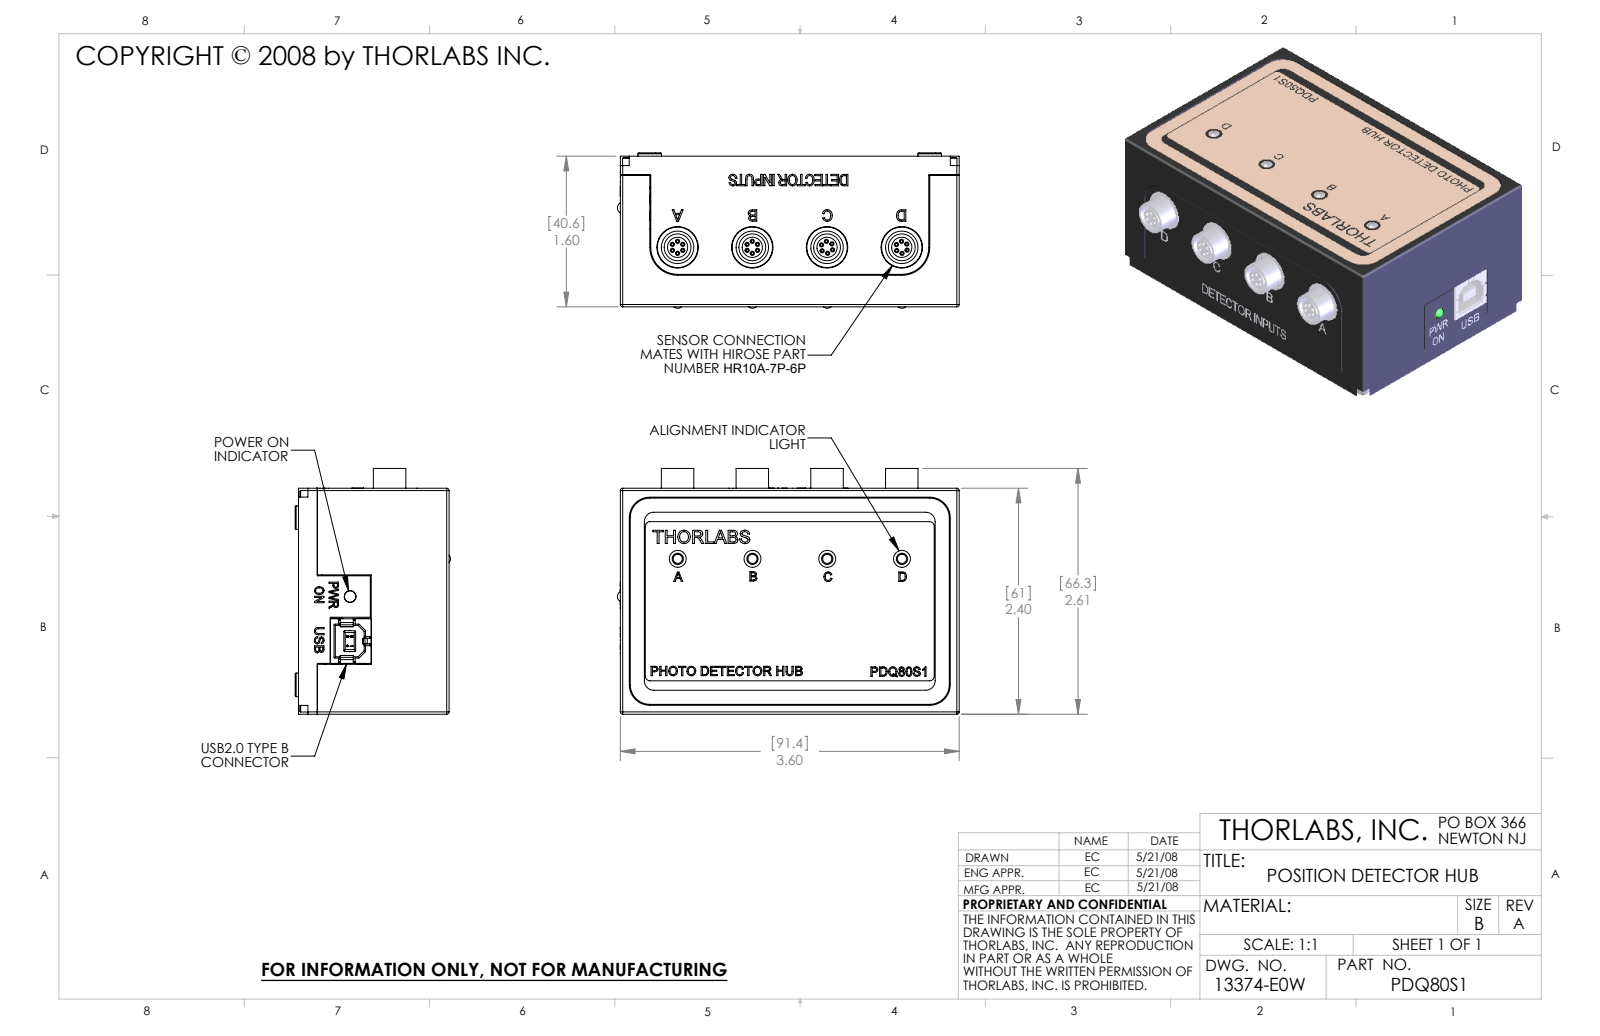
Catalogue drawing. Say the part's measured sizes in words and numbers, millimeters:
The part is named "13374-E0W". Its 3-D file was written by "SolidWorks 2007 (CONFIG_CONTROL_DESIGN)". It is 17 solids with 2142 faces: 1275 planar, 369 cylindrical and 498 other. Overall it measures 92.23 by 66.29 by 41.91 millimeters. Its volume is 57 288 cubic millimeters and its surface area 61 288 square millimeters. Round holes: 12 of diameter 0.63, 12 of diameter 0.64, 6 of diameter 1.78, 6 of diameter 2.18, 4 of diameter 2.39, 4 of diameter 2.84, 4 of diameter 3.05, 4 of diameter 3.3, 4 of diameter 6.35, 4 of diameter 6.6, 4 of diameter 7.24, 4 of diameter 8.2. Round bosses or shafts: 4 of diameter 10.92, 4 of diameter 8.76, 4 of diameter 4.57, 4 of diameter 3.56, 3 of diameter 5.46, 1 of diameter 5.46, 1 of diameter 3.91, 1 of diameter 3.51. Partial cylindrical surfaces (rounded edges, fillets, slot ends): 20 of radius 0.25, 8 of radius 0.13, 8 of radius 0.64, 8 of radius 4.13, 7 of radius 5.4, 6 of radius 1.27, 4 of radius 0.2, 4 of radius 0.3. The main face-to-face distances are 40.26, 38.1, 2.16, 40.39, 2.29, 1.91, 36.19, 38.35, 38.48, 60.96. The hole center spacings are 1.62, 2.81, 18.78, 21.59, 1.63, 2.8, 3.24, 20.17.
